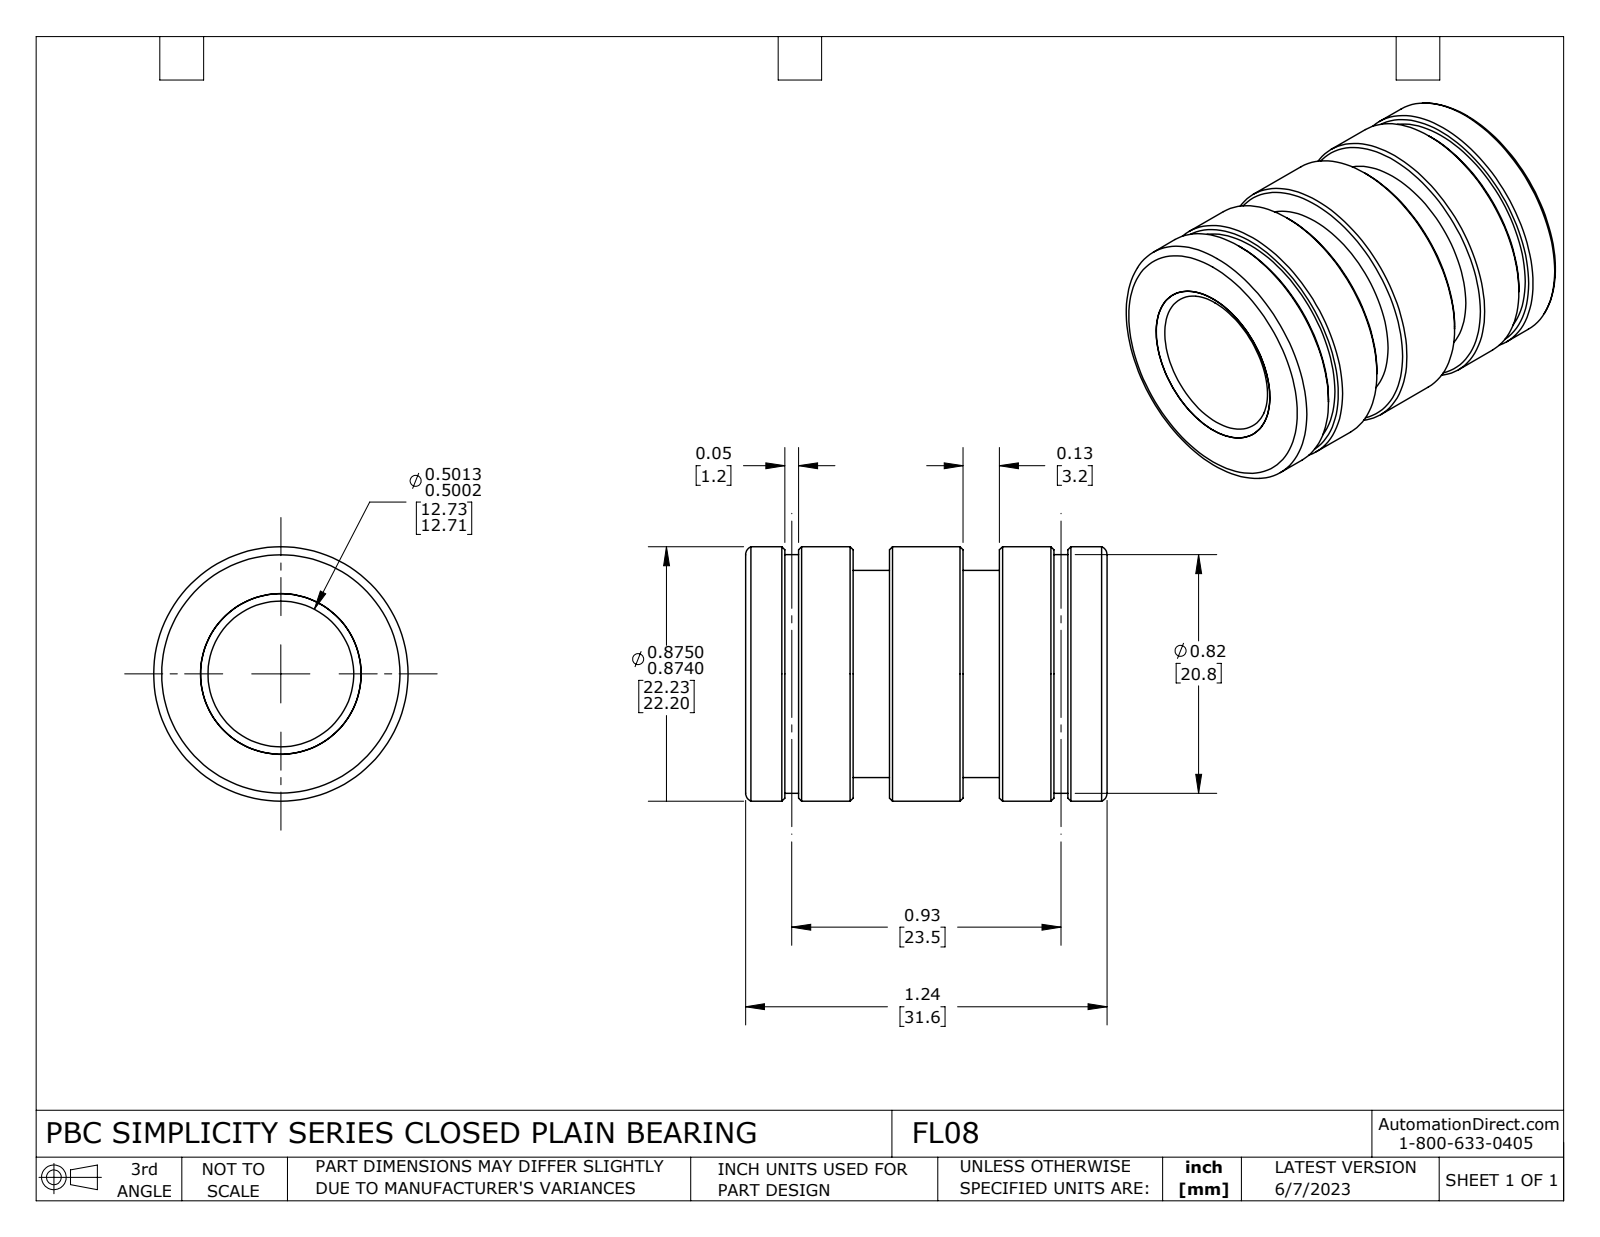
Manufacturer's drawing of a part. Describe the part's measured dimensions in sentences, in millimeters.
The part is named "FL08". Its 3-D file was written by "SolidWorks 2021 (CONFIG_CONTROL_DESIGN)". It is 2 solids with 58 faces: 10 planar, 24 cylindrical and 24 other. Overall it measures 31.6 by 22.2 by 22.2 millimeters. Its volume is 7 230 cubic millimeters and its surface area 7 232 square millimeters. Round holes: 1 of diameter 12.7, 1 of diameter 14. Round bosses or shafts: 1 of diameter 22.2, 1 of diameter 20.8, 1 of diameter 18.1. The main face-to-face distances are 9.4, 12.6, 19, 22.2, 3.2, 9.6, 31.6, 12.8, 6.4, 3.4.
